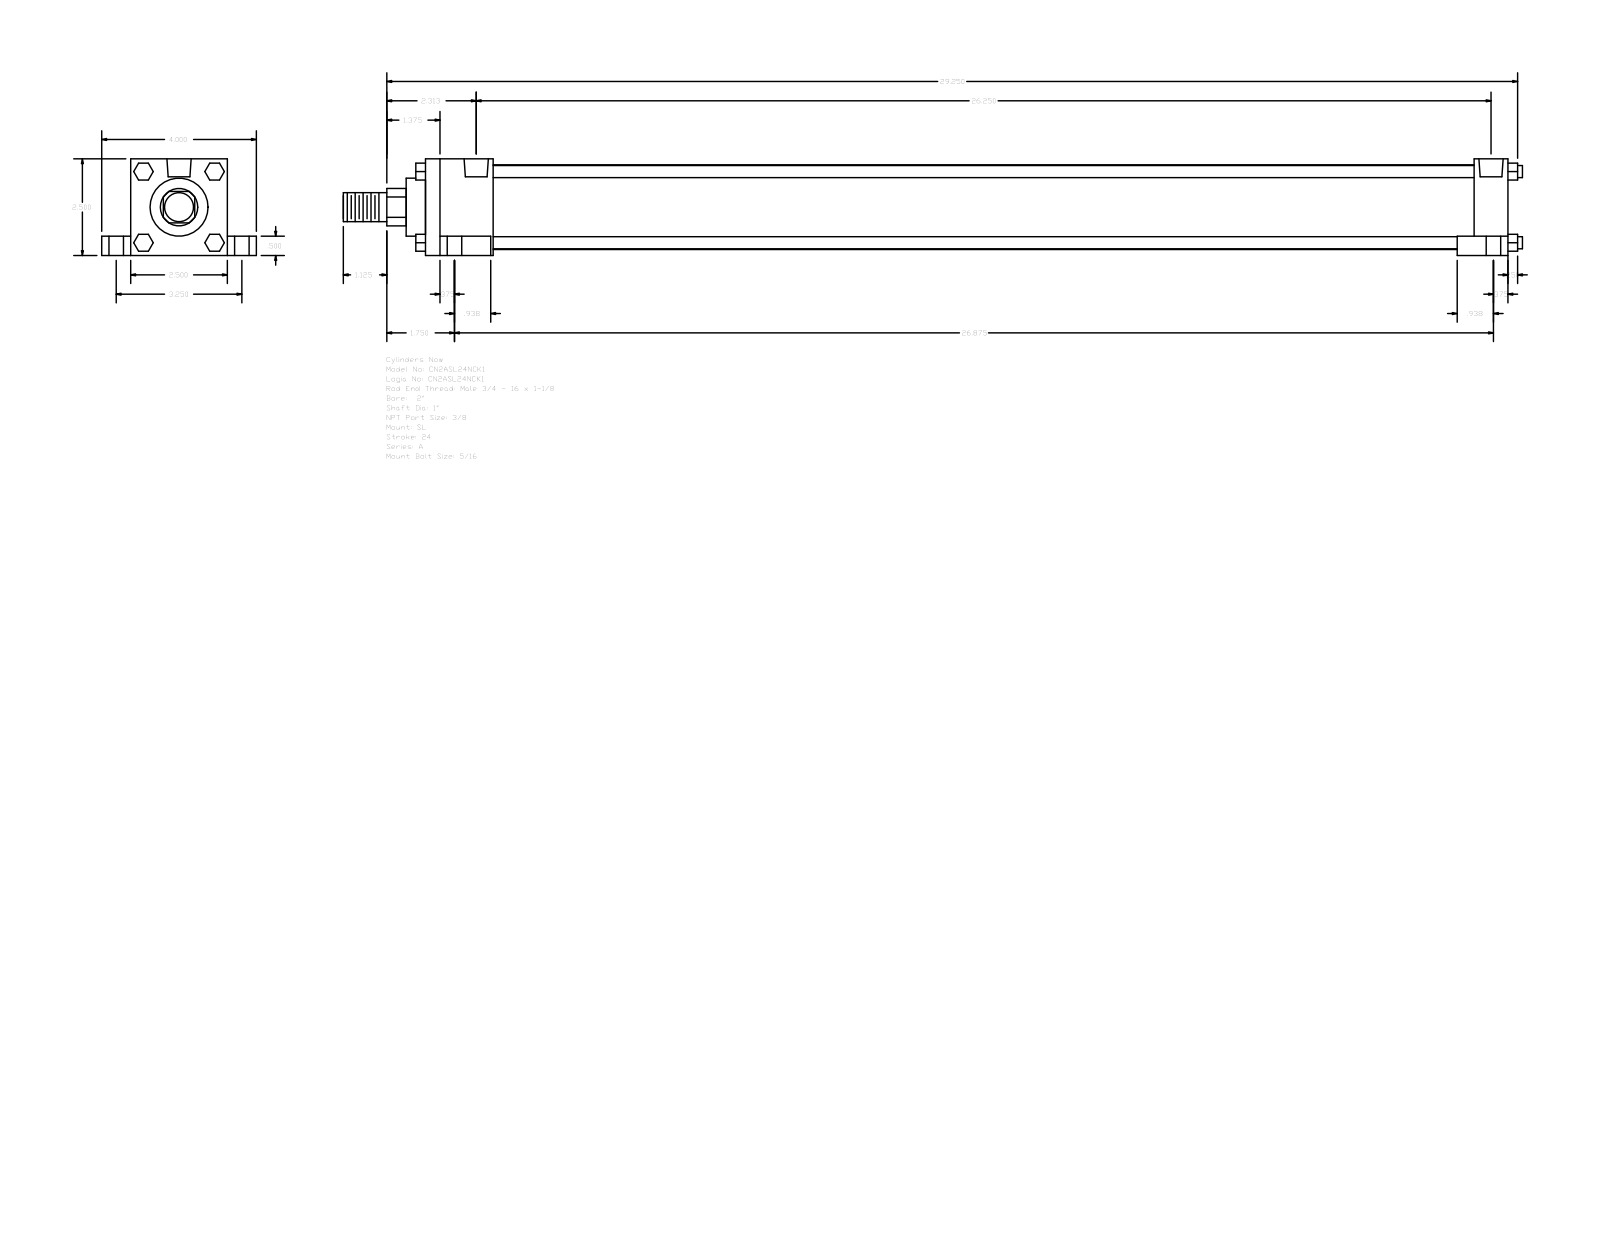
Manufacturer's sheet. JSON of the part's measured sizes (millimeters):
{"part_name": "A_SL__0200_1", "step_written_by": "GSSL Pune (CONFIG_CONTROL_DESIGN)", "units": "millimeters", "bodies": {"solids": 0, "faces": 148, "planar": 112, "cylindrical": 36, "other": 0}, "overall_size": [774.7, 101.6, 63.5], "round_holes": [[5.56, 4], [9.53, 4], [15.88, 4], [15.93, 2]], "round_bosses_or_shafts": [[7.94, 4], [55.63, 1], [38.1, 1], [25.4, 1], [19.05, 1]], "partial_cylinders_radius": [[12.29, 1]], "face_to_face_distances": [63.5, 711.2, 12.7, 50.8, 22.22, 19.05, 82.55, 44.45, 666.75, 688.98], "hole_center_spacings": [41.3, 41.64, 43.67, 44.22, 82.54, 661.18, 668.03, 669.61]}
